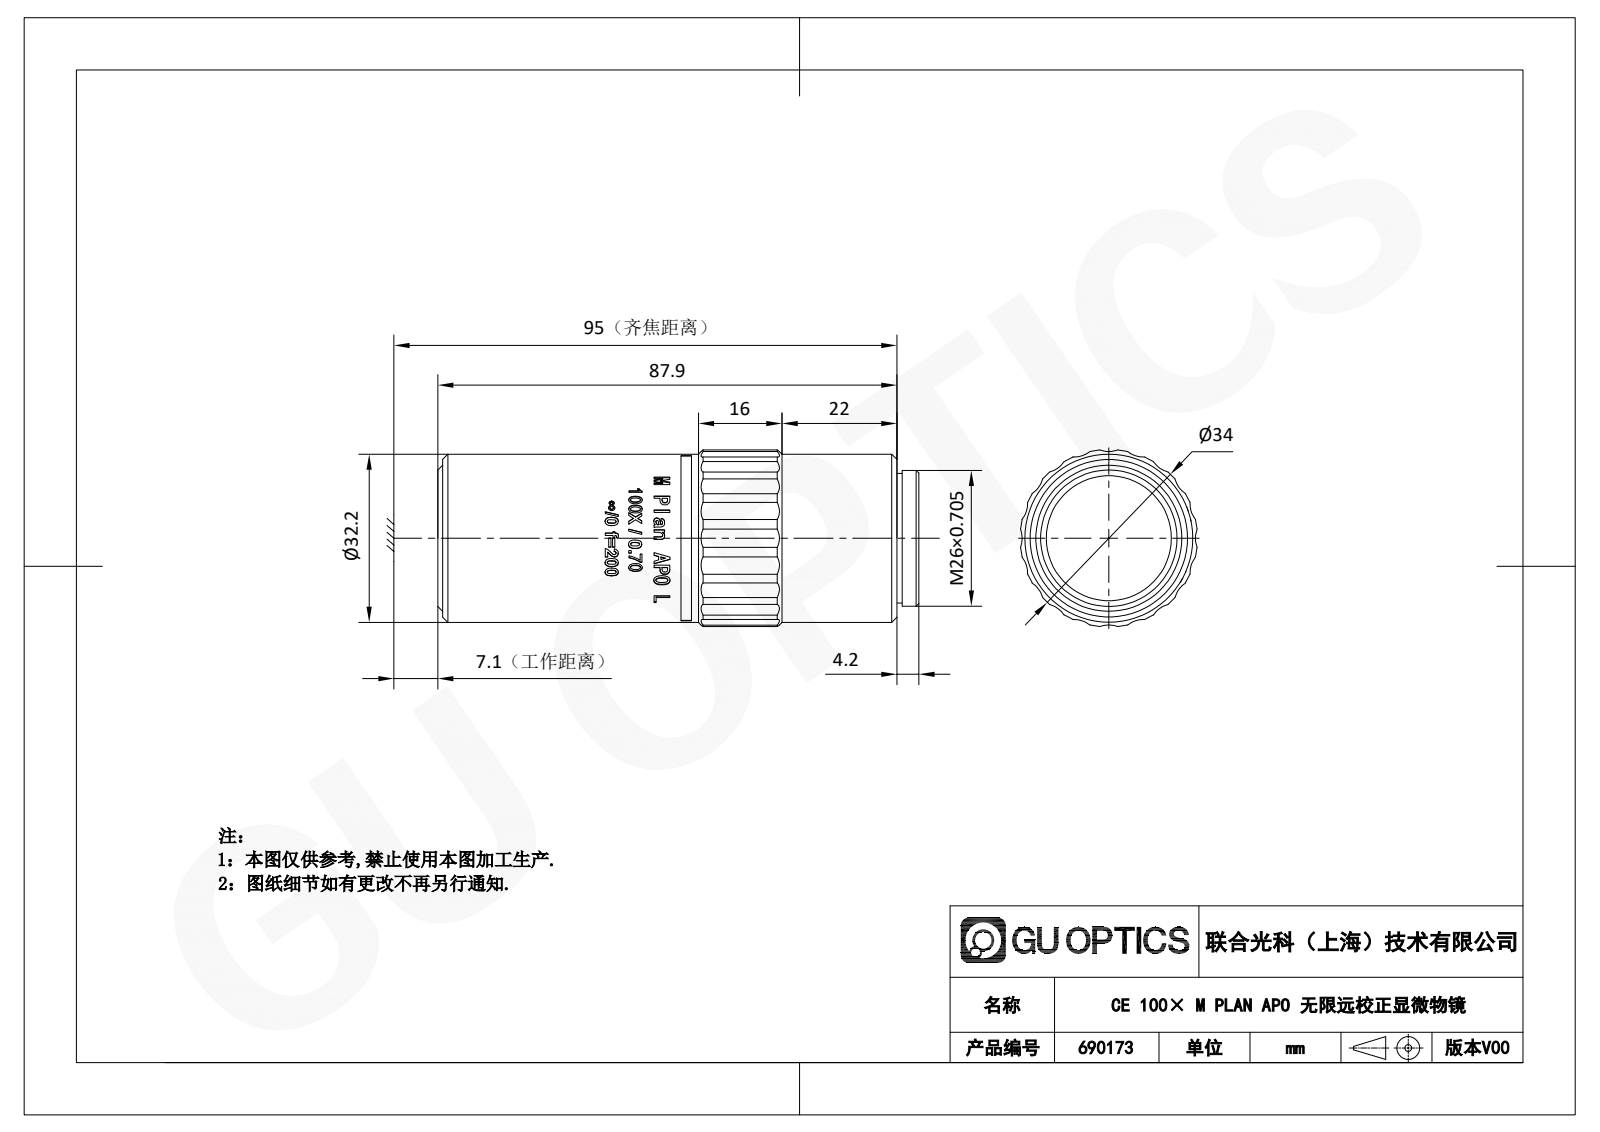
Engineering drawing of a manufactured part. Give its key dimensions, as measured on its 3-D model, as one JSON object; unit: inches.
{"part_name": "690168", "step_written_by": "SolidWorks 2020 (CONFIG_CONTROL_DESIGN)", "units": "inches", "bodies": {"solids": 1, "faces": 378, "planar": 111, "cylindrical": 98, "other": 169}, "overall_size": [3.626, 1.331, 1.331], "volume_in3": 4.468, "surface_area_in2": 17.38, "round_holes": [[0.866, 1], [0.945, 1]], "round_bosses_or_shafts": [[1.268, 1], [1.26, 1], [1.024, 1], [0.976, 1]], "partial_cylinders_radius": [[0.197, 20], [0.626, 1], [0.669, 1]], "face_to_face_distances": [3.492, 0.051, 3.441, 0.114, 0.165, 3.606, 3.589, 3.475, 3.424, 0.017]}
